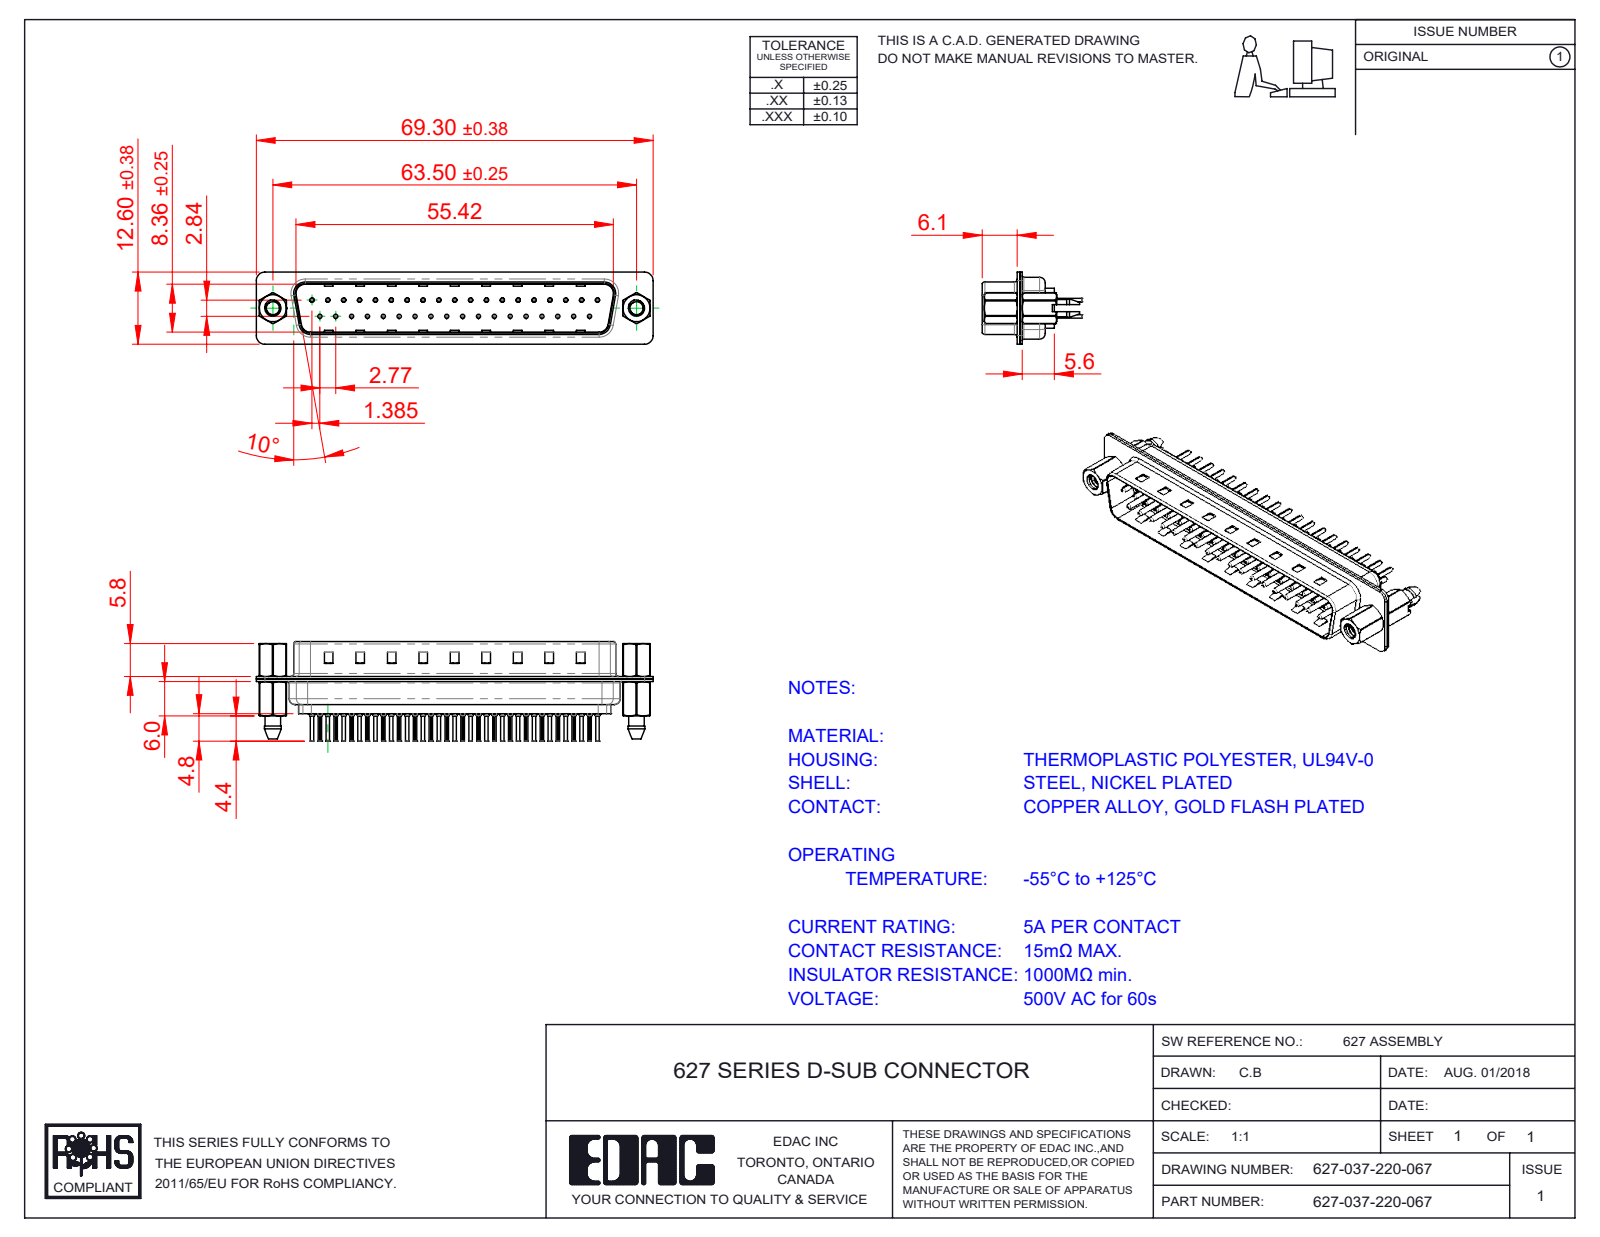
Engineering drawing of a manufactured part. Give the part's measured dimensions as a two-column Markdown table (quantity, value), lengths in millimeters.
| quantity | value |
| --- | --- |
| part name | 627 4-40 Threaded Boardlock_LP; 627-037-220-067; 627 Shell Rear_37 Contacts; 627 Contact Row 1_20L (+4 more) |
| STEP written by | SolidWorks 2020 (CONFIG_CONTROL_DESIGN) |
| units | millimeters |
| bodies | 44 solids, 4238 faces (1145 planar, 1614 cylindrical, 1479 other) |
| overall size | 69.3 × 17.3 × 12.6 |
| volume | 4 028 mm³ |
| surface area | 11 455 mm² |
| round holes (diameter × count) | 0.2 × 37, 0.35 × 37, 1.1 × 37, 1.6 × 37, 2.26 × 2, 2.29 × 2, 4 × 2, 4.8 × 2 |
| round bosses / shafts (diameter × count) | 2 × 37, 1.5 × 37, 0.75 × 37, 0.6 × 37, 4.9 × 2, 2.79 × 2 |
| partial cylindrical surfaces (radius × count) | 0.1 × 74, 1.5 × 18, 2 × 12, 1.6 × 10, 0.5 × 8, 0.25 × 4, 0.6 × 4, 0.65 × 4 |
| main face-to-face distances | 0.4, 0.82, 9.58, 0.45, 8.76, 1.5, 0.9, 1.4, 6.5, 6.05 |
| hole center spacings | 3.16, 2.77, 5.54, 8.31, 5.04, 10.1, 11.08, 12.78 |
